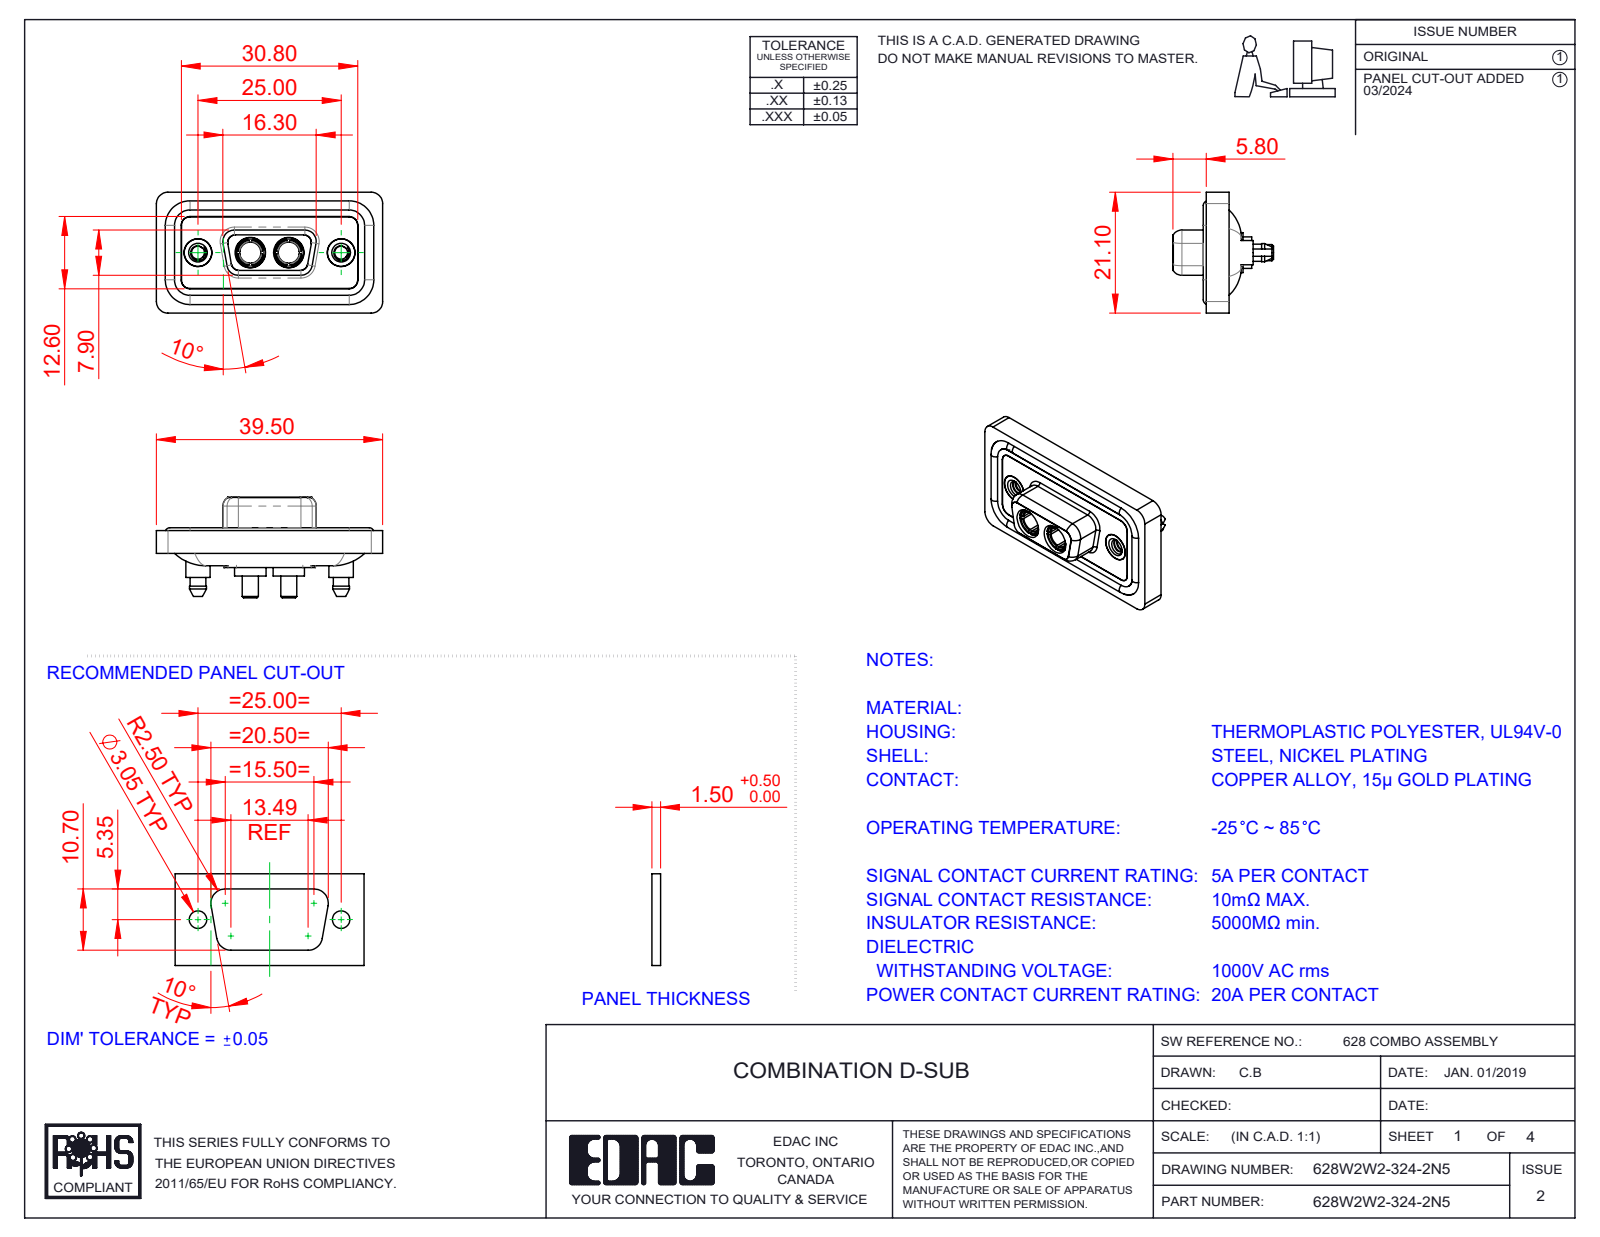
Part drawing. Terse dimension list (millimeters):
name: Power Socket_20A S; 628Combo Waterproof Housing_09 Contacts; 628Combo Shell Front_09 Contacts; 628Combo Shell Rear_09 Contacts (+3 more)
written by: SolidWorks 2023 (CONFIG_CONTROL_DESIGN)
unit: mm
bodies: 11 solids, 584 faces (179 planar, 266 cylindrical, 139 other)
size: 39.5 × 21.1 × 17.55
volume: 4 846 mm³; area: 7 969 mm²
holes: 4× ⌀4.85, 2× ⌀2.26, 2× ⌀3.7, 2× ⌀4, 2× ⌀4.05, 2× ⌀5, 2× ⌀5.3
bosses: 4× ⌀1.6, 2× ⌀5.5, 2× ⌀5.4, 2× ⌀5.2, 2× ⌀4.96, 2× ⌀4.95, 2× ⌀4.8, 2× ⌀4.75
rounds: 24× R1.5, 18× R2, 10× R1.6, 8× R1.35, 4× R0.25, 4× R0.5, 4× R0.6, 4× R0.65
face distances: 0.4, 1.8, 1.1, 2.9, 1.6, 0.5, 5.65, 7.45, 1.5, 4
hole spacings: 9.14, 15.86, 6.72, 25
